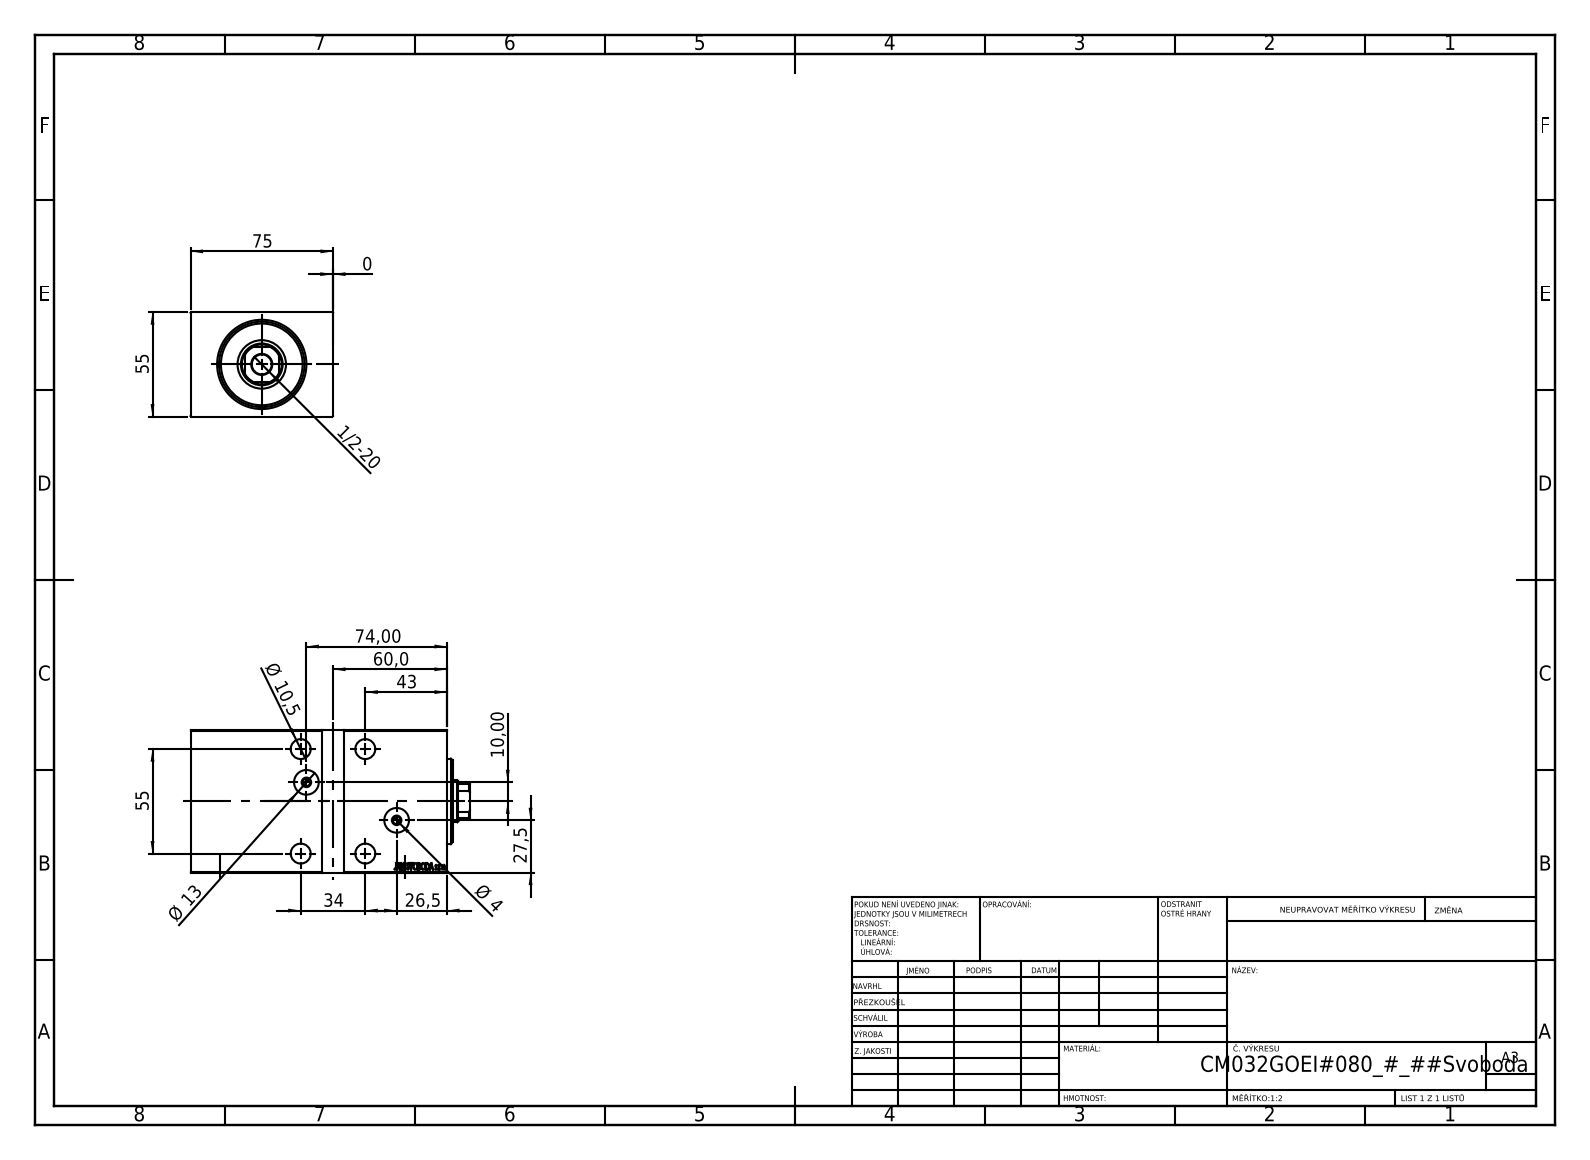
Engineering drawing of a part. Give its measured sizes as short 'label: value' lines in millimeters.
name: V450CM_VC_G; V450CM_G_VCP; Zatka_OIL_PORT; V450CM_G_Body
written by: SolidWorks 2019 (CONFIG_CONTROL_DESIGN)
unit: mm
bodies: 5 solids, 896 faces (442 planar, 56 cylindrical, 398 other)
size: 147 × 75 × 55
volume: 498 699 mm³; area: 83 816 mm²
holes: 5× ⌀10.5, 4× ⌀16.5, 2× ⌀4, 2× ⌀13, 1× ⌀22, 1× ⌀25.5, 1× ⌀32, 1× ⌀34, 1× ⌀45
bosses: 2× ⌀18, 2× ⌀5, 1× ⌀27
rounds: 1× R10.5
face distances: 55, 75, 135, 5, 3, 130, 125, 10, 120, 138
hole spacings: 34, 55, 64.66, 17.76, 24.05, 35.6, 37.62, 40.97
